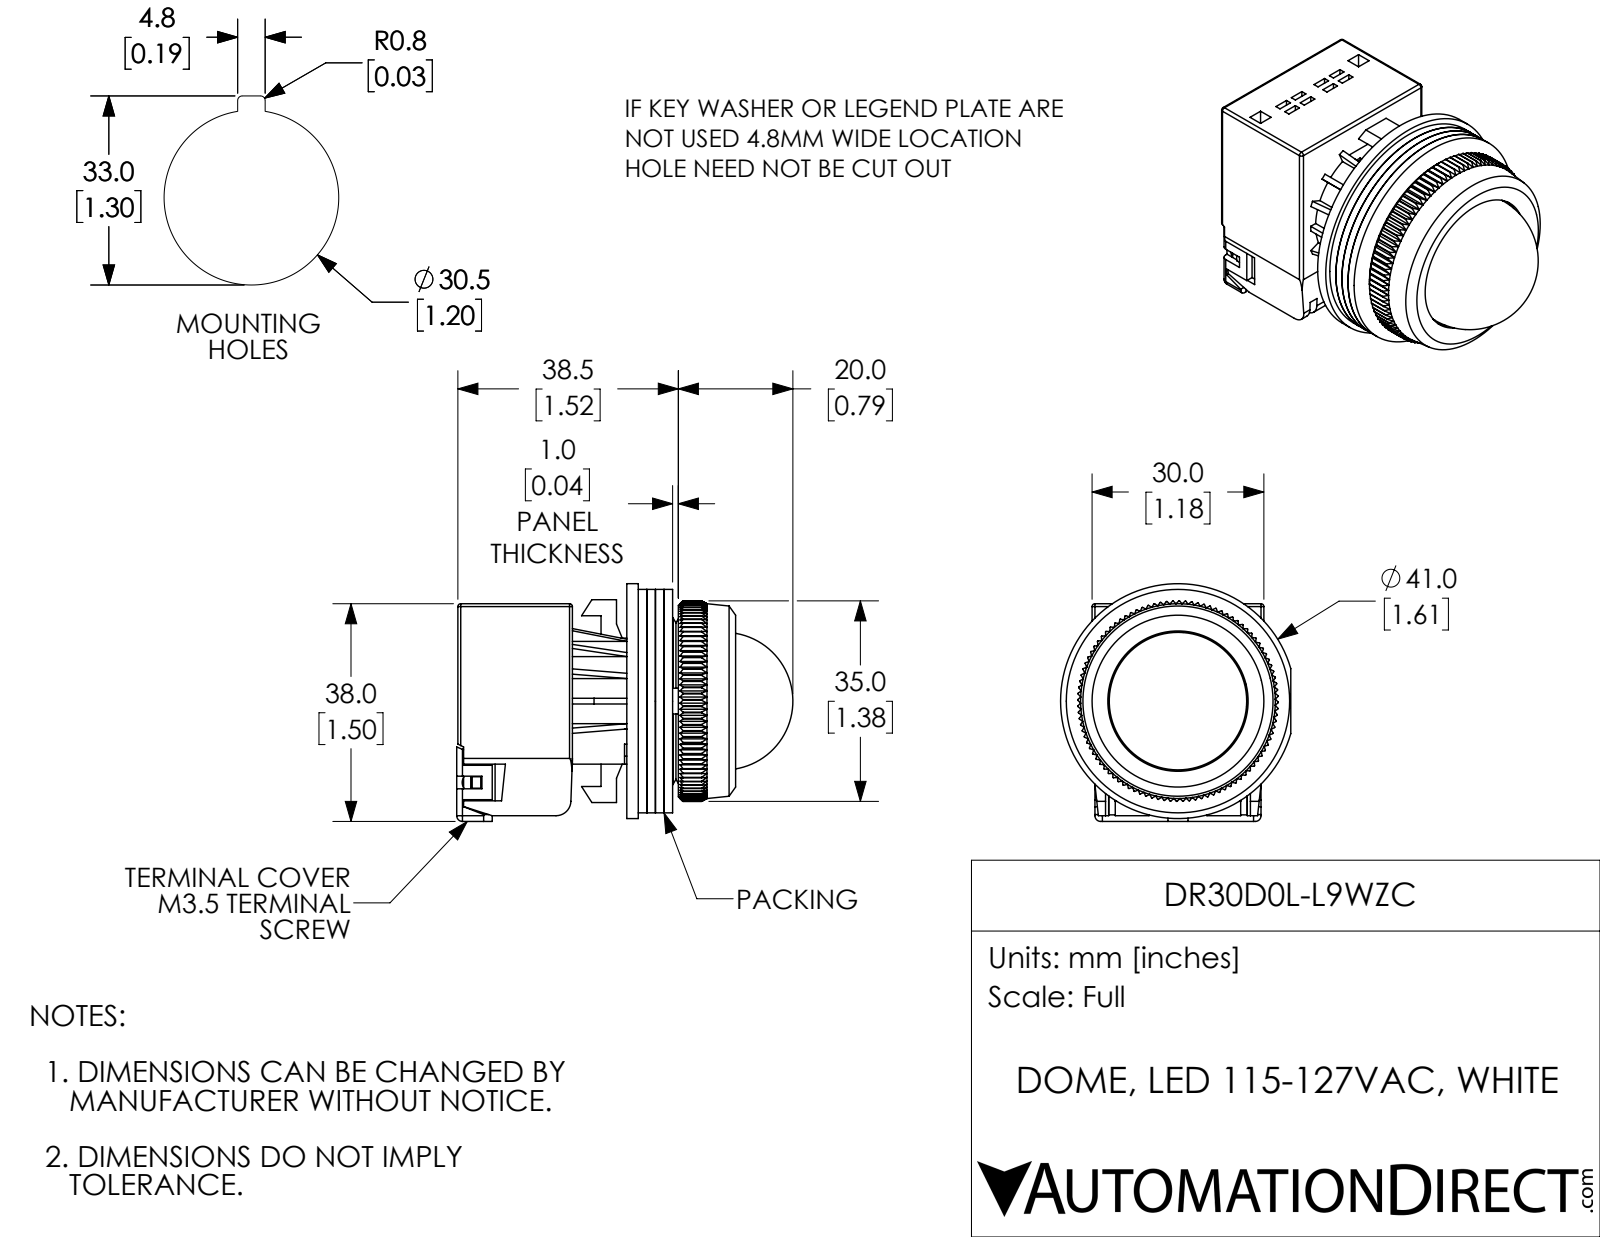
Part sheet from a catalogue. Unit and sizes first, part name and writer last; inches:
Units: inches
Overall size (bounding box): 2.309 × 1.634 × 1.583
Round holes (diameter × count): ⌀0.118 ×2, ⌀0.122 ×2, ⌀0.138 ×2, ⌀0.276 ×2, ⌀0.362 ×1, ⌀0.433 ×1, ⌀0.461 ×1, ⌀0.543 ×1, ⌀0.563 ×1, ⌀0.583 ×1, ⌀0.63 ×1, ⌀0.72 ×1
Round bosses / shafts (diameter × count): ⌀0.232 ×2, ⌀1.614 ×1, ⌀1.535 ×1, ⌀1.16 ×1, ⌀0.945 ×1, ⌀0.858 ×1, ⌀0.819 ×1, ⌀0.799 ×1
Partial cylindrical surfaces — rounded edges, fillets, slot ends (radius × count): R0.039 ×14, R0.008 ×8, R0.02 ×8, R0.065 ×3, R0.029 ×1, R0.068 ×1, R0.079 ×1, R0.102 ×1
Main face-to-face distances: 0.059, 0.118, 0.177, 0.039, 0.315, 0.197, 0.512, 0.689, 0.374, 1.161
Hole centre spacings: 0.704, 0.63
Volume: 2.184 in³ · Surface area: 48.71 in²
Bodies: 18 solids, 1544 faces (945 planar, 353 cylindrical, 246 other)
Part name (STEP PRODUCT): DR30D0L-L9WZC
STEP written by: SolidWorks 2017 (AUTOMOTIVE_DESIGN)
